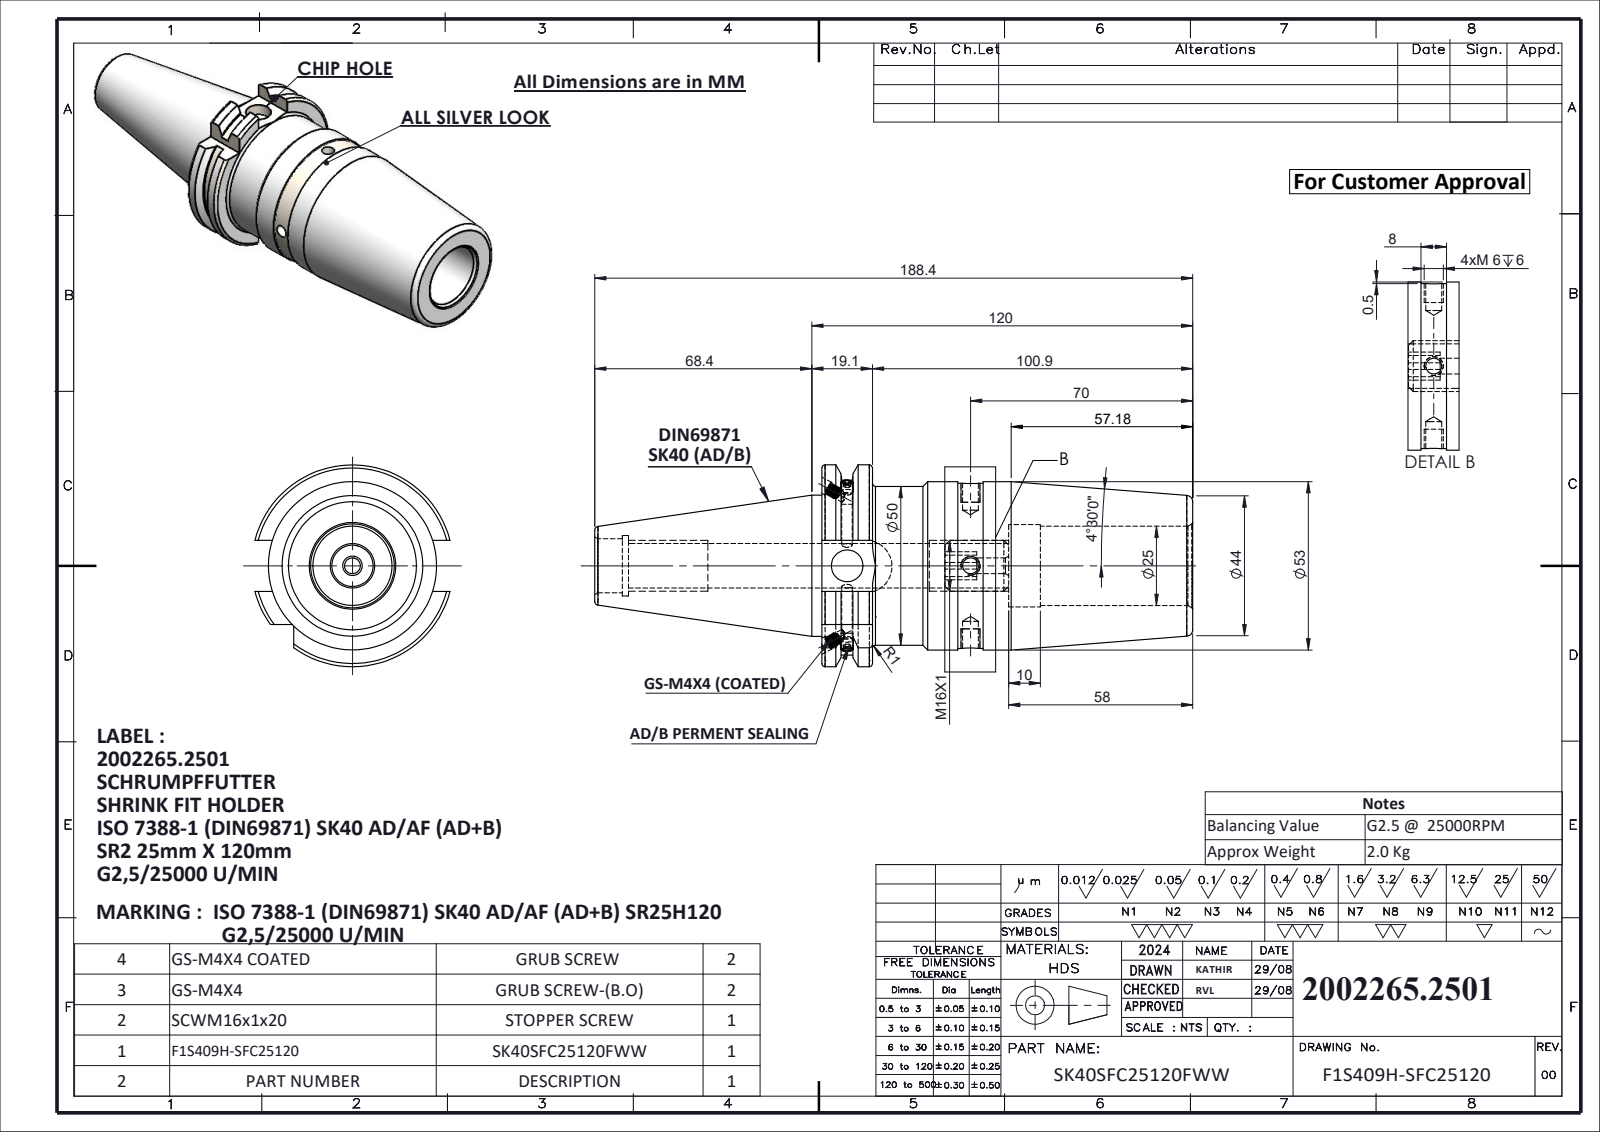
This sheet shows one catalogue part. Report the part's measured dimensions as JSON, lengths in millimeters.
{"part_name": "SCWM16X1P; F1S409H-SFC25120; SK40SFC25120F-FIN; GS-M4X4_DIN 913 - M4 x 4-N (+1 more)", "step_written_by": "SolidWorks 2024 (CONFIG_CONTROL_DESIGN)", "units": "millimeters", "bodies": {"solids": 6, "faces": 287, "planar": 77, "cylindrical": 88, "other": 122}, "overall_size": [188.4, 63.55, 61.48], "volume_mm3": 262921, "surface_area_mm2": 45909, "round_holes": [[3.3, 3], [5, 3], [4.5, 2], [10, 1], [14, 1], [17, 1], [19, 1], [24.98, 1], [25.98, 1]], "round_bosses_or_shafts": [[4, 4], [2.9, 2], [53, 1], [52, 1], [50, 1], [44.45, 1], [16, 1]], "partial_cylinders_radius": [[8.25, 1], [28.12, 1], [31.77, 1]], "face_to_face_distances": [116.8, 15.9, 100.9, 58.8, 42.9, 58, 8, 47.8, 16.1, 3.62], "hole_center_spacings": [38.85]}
